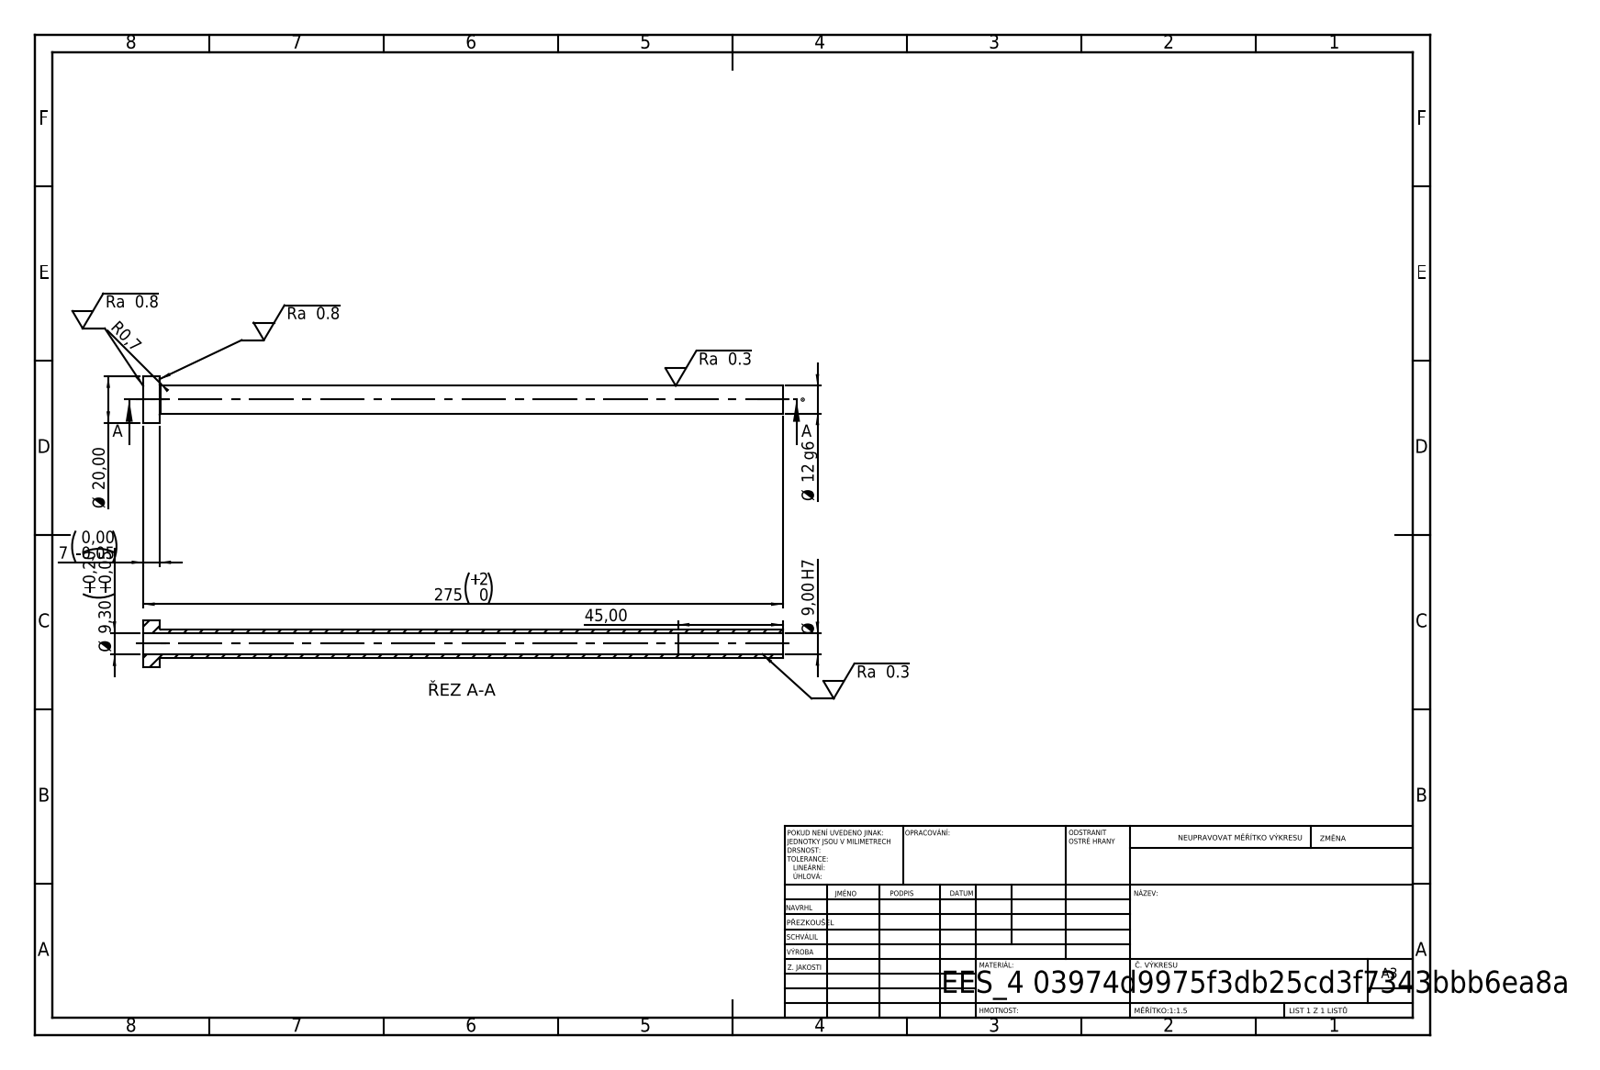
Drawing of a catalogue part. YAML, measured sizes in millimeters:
step_written_by: "SolidWorks 2019 (CONFIG_CONTROL_DESIGN)"
units: millimeters
bodies: {solids: 1, faces: 14, planar: 4, cylindrical: 8, other: 2}
overall_size: [275, 20, 20]
volume: 14027
surface_area: 19025
round_holes:
  - {diameter: 9, count: 1}
  - {diameter: 9.3, count: 1}
round_bosses_or_shafts:
  - {diameter: 20, count: 1}
  - {diameter: 12, count: 1}
face_to_face_distances: [7, 275, 268, 230, 223, 45]
